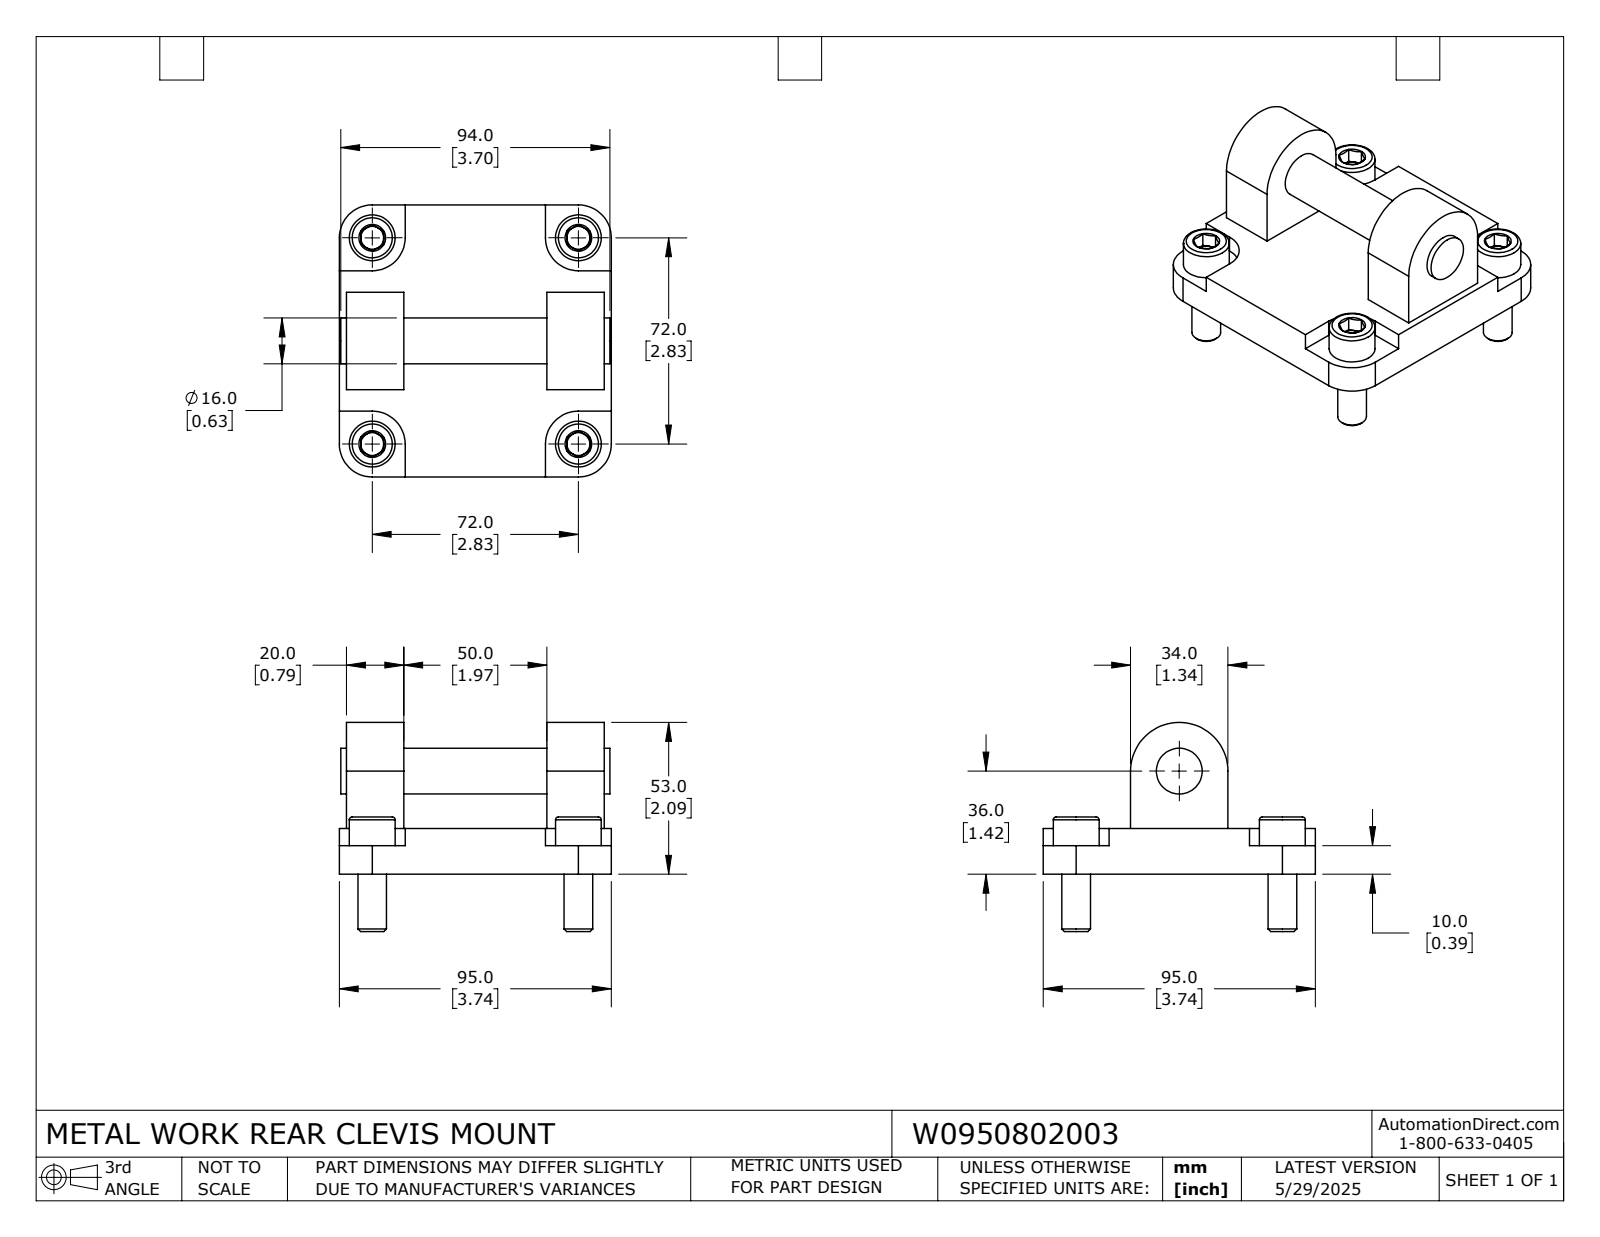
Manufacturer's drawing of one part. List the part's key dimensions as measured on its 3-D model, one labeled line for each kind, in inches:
Part name (STEP PRODUCT): W0950802003
STEP written by: SolidWorks 2024 (CONFIG_CONTROL_DESIGN)
Units: inches
Bodies: 5 solids, 187 faces (89 planar, 42 cylindrical, 56 other)
Overall size (bounding box): 3.74 × 3.74 × 2.874
Volume: 11.32 in³ · Surface area: 65.81 in²
Round holes (diameter × count): ⌀0.433 ×4, ⌀1.772 ×1
Round bosses / shafts (diameter × count): ⌀0.63 ×5, ⌀0.394 ×4
Partial cylindrical surfaces — rounded edges, fillets, slot ends (radius × count): R0.453 ×4, R0.669 ×1
Main face-to-face distances: 0.63, 0.787, 0.394, 0.886, 3.74, 0.236, 2.854, 0.098, 3.642, 2.756
Hole centre spacings: 2.004, 2.835, 4.009
